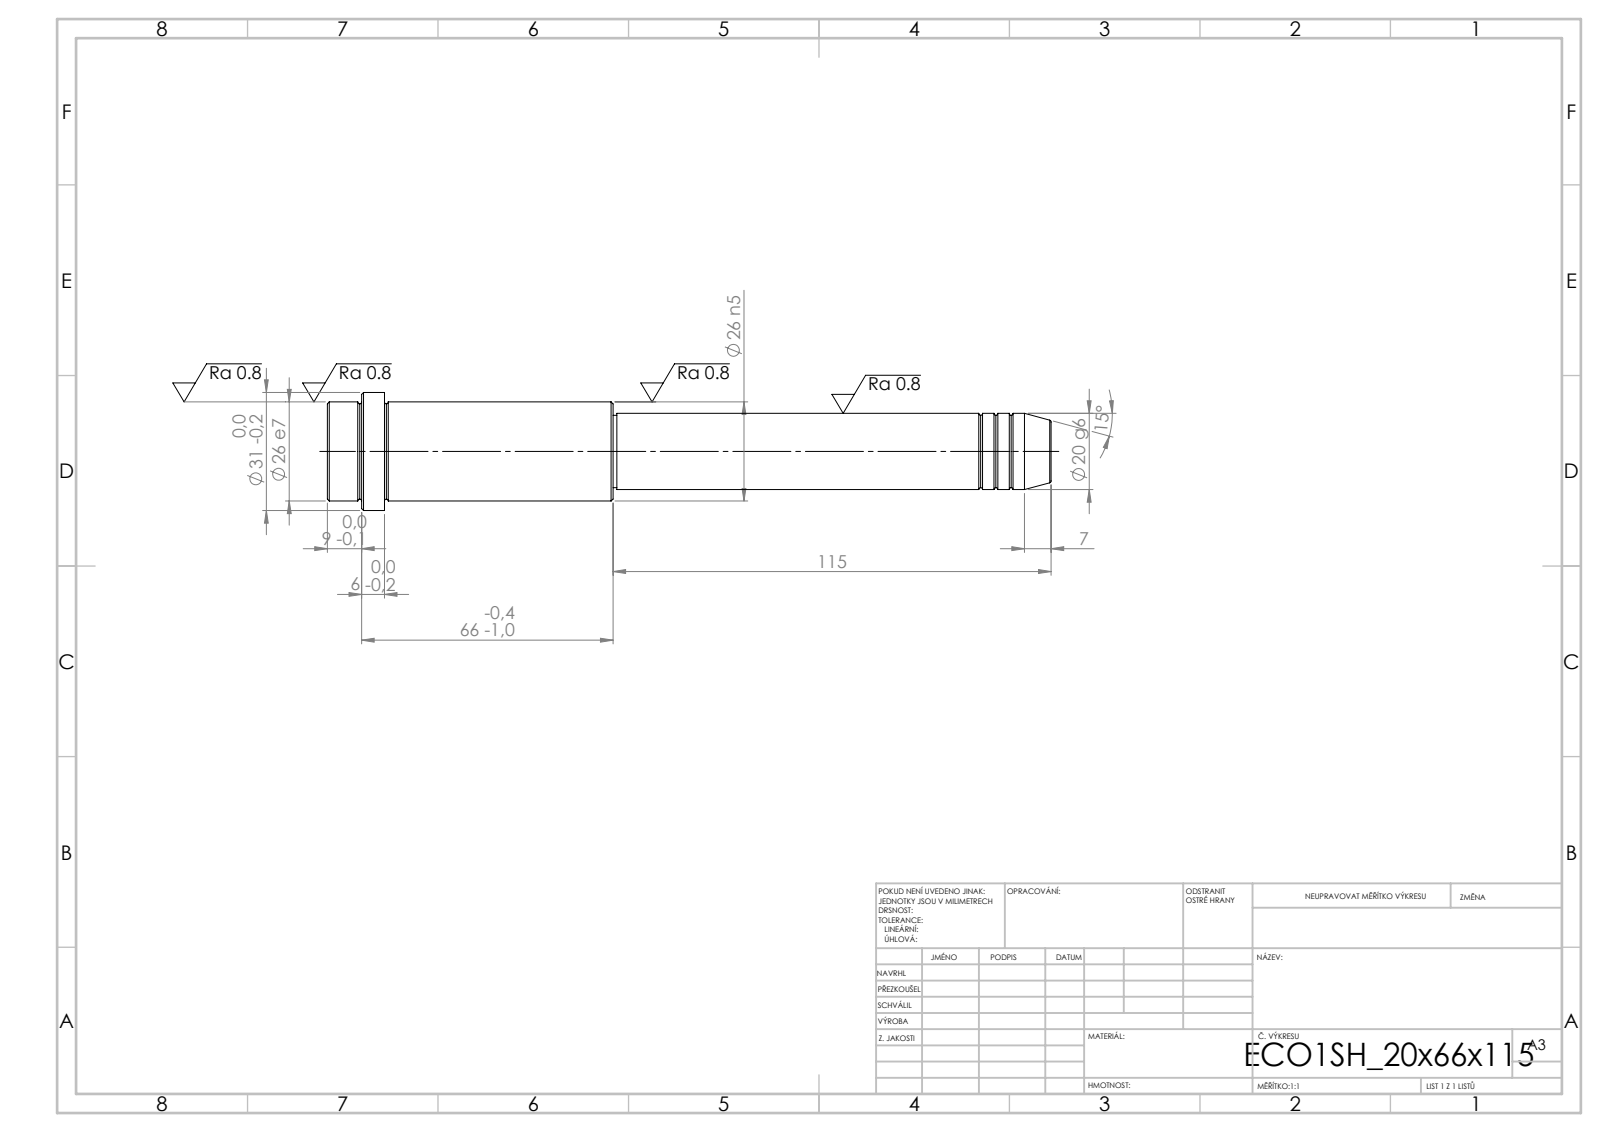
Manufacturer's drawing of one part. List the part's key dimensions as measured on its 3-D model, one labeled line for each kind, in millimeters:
STEP written by: SolidWorks 2019 (CONFIG_CONTROL_DESIGN)
Units: millimetres
Bodies: 1 solid, 52 faces (6 planar, 16 cylindrical, 30 other)
Overall size (bounding box): 190 × 31 × 31
Volume: 76 705 mm³ · Surface area: 14 982 mm²
Round bosses / shafts (diameter × count): ⌀31 ×1, ⌀26 ×1, ⌀20 ×1, ⌀19 ×1
Main face-to-face distances: 15, 60, 75, 115, 175, 190, 181, 66, 6, 9
